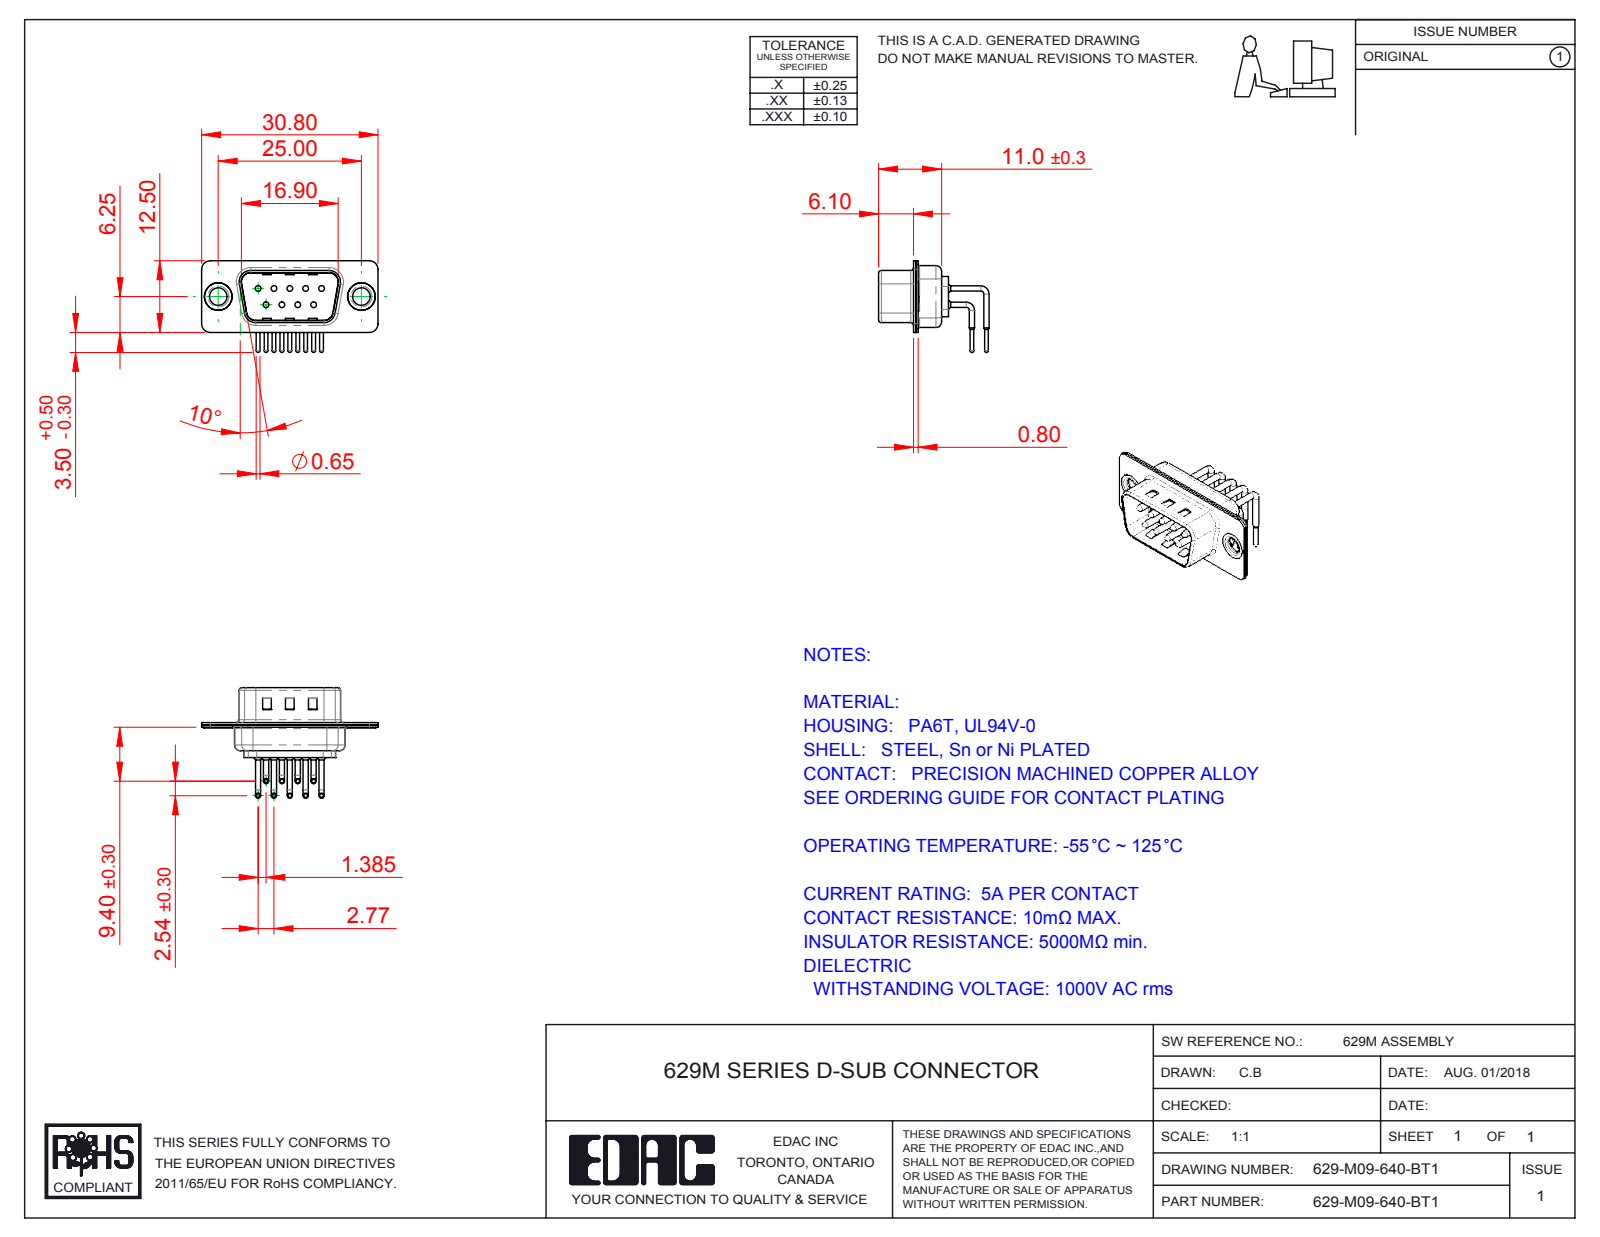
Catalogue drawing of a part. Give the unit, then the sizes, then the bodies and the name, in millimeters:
Units: millimetres
Overall size (bounding box): 30.8 × 19.29 × 16
Round holes (diameter × count): ⌀1 ×9, ⌀1.7 ×9, ⌀2 ×9, ⌀3.05 ×2, ⌀4 ×2, ⌀4.8 ×2
Round bosses / shafts (diameter × count): ⌀0.9 ×18, ⌀1.5 ×9, ⌀0.65 ×9, ⌀5 ×2, ⌀4.9 ×2, ⌀3.55 ×2
Partial cylindrical surfaces — rounded edges, fillets, slot ends (radius × count): R1.5 ×16, R2 ×12, R1.01 ×9, R0.5 ×8, R1.6 ×8, R0.25 ×4, R0.6 ×4, R0.65 ×4
Main face-to-face distances: 0.4, 0.85, 0.8, 9.55, 1.25, 10.4, 8.7, 0.35, 6.1, 5.7
Hole centre spacings: 3.16, 2.77, 5.54, 5.03, 5.04, 8.31, 7.1, 7.48
Volume: 1 302 mm³ · Surface area: 3 762 mm²
Bodies: 14 solids, 1268 faces (683 planar, 437 cylindrical, 148 other)
Part name (STEP PRODUCT): 629M Shell Front_09 Contacts; 629M Housing_09 Contacts; 629M Shell Rear_09 Contacts; 629M Thru Hole Rivet (+3 more)
STEP written by: SolidWorks 2016 (CONFIG_CONTROL_DESIGN)
